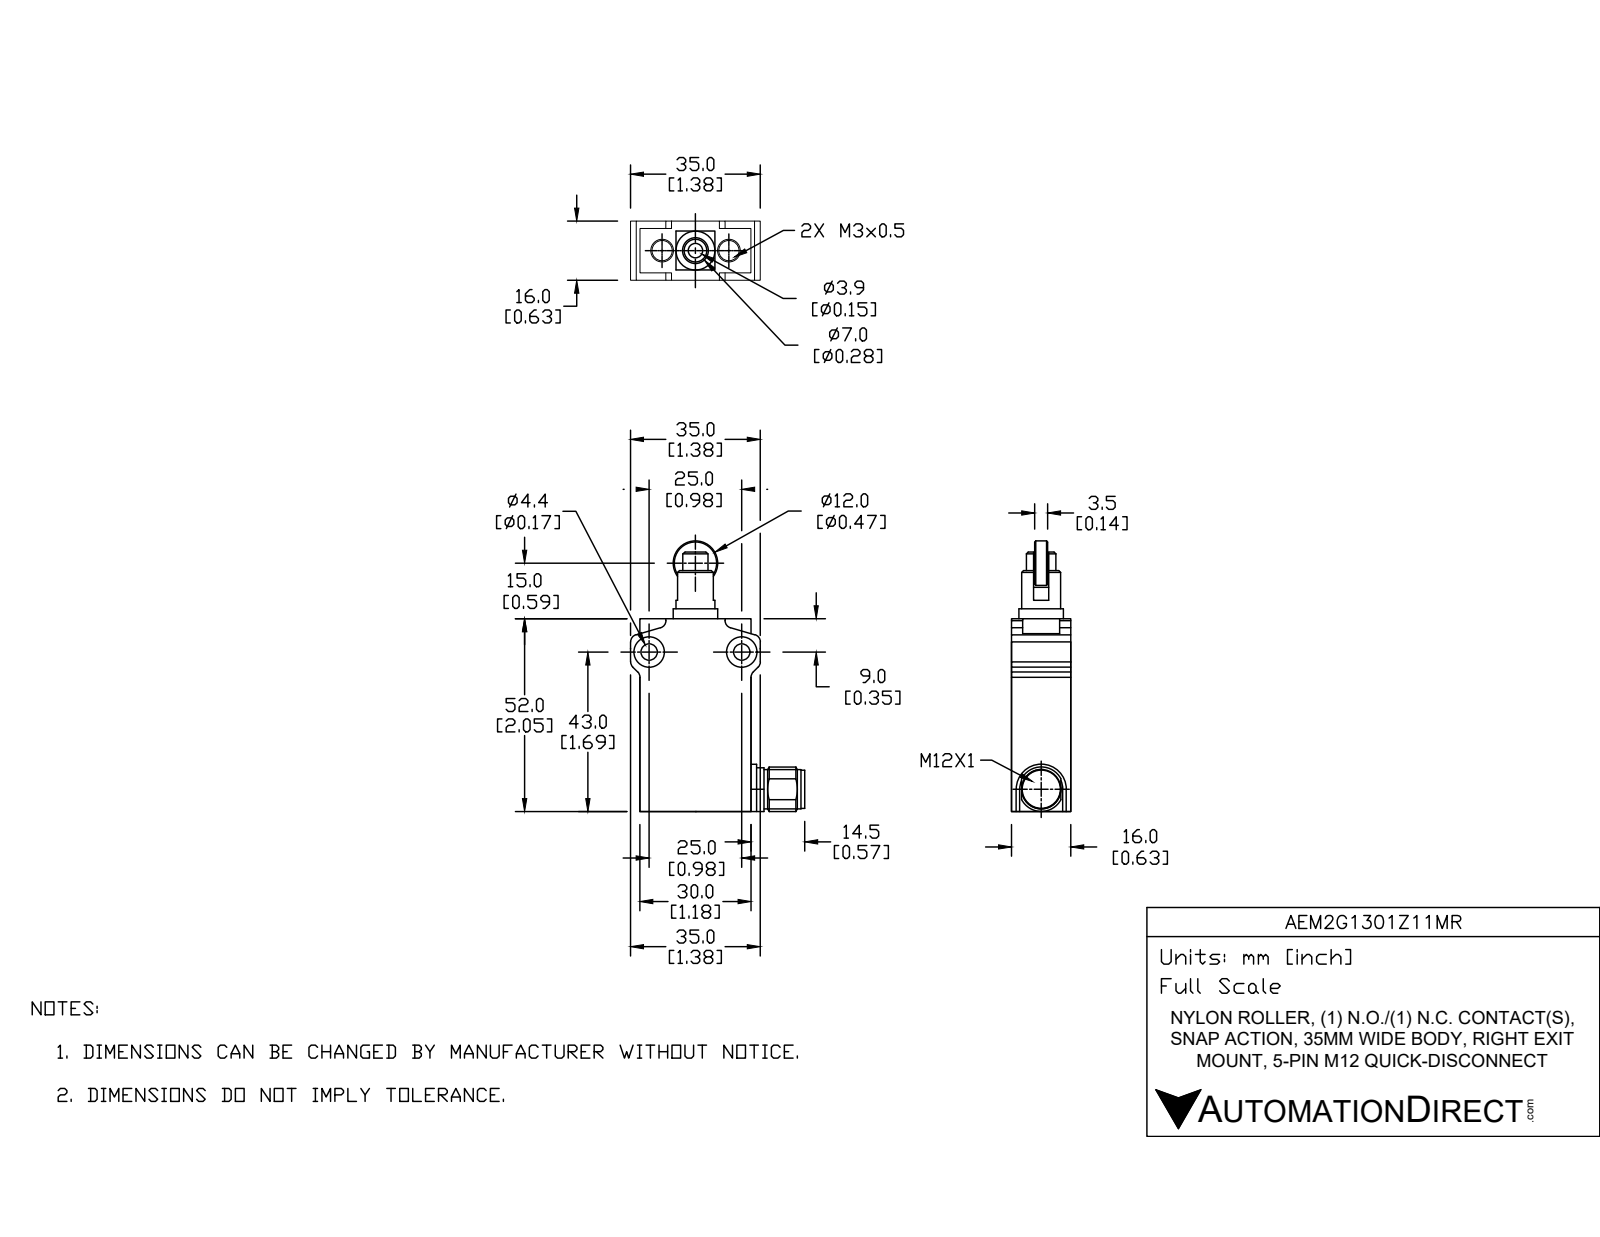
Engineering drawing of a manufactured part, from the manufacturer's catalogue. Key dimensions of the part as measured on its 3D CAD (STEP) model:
Part name (STEP PRODUCT): AEM2G1301Z11MR
STEP written by: SolidWorks 2019 (AUTOMOTIVE_DESIGN)
Units: inches
Bodies: 5 solids, 157 faces (68 planar, 51 cylindrical, 38 other)
Overall size (bounding box): 2.878 × 1.831 × 0.63
Volume: 1.644 in³ · Surface area: 14.91 in²
Round holes (diameter × count): ⌀0.118 ×2, ⌀0.173 ×2, ⌀0.323 ×2, ⌀0.317 ×1
Round bosses / shafts (diameter × count): ⌀0.472 ×3, ⌀0.417 ×1, ⌀0.413 ×1, ⌀0.406 ×1, ⌀0.313 ×1, ⌀0.22 ×1
Partial cylindrical surfaces — rounded edges, fillets, slot ends (radius × count): R0.079 ×8, R0.256 ×1
Main face-to-face distances: 0.63, 1.181, 2.047, 0.472, 0.234, 0.157, 0.238, 0.15, 0.396, 0.098
Hole centre spacings: 0.374, 0.748, 0.984
